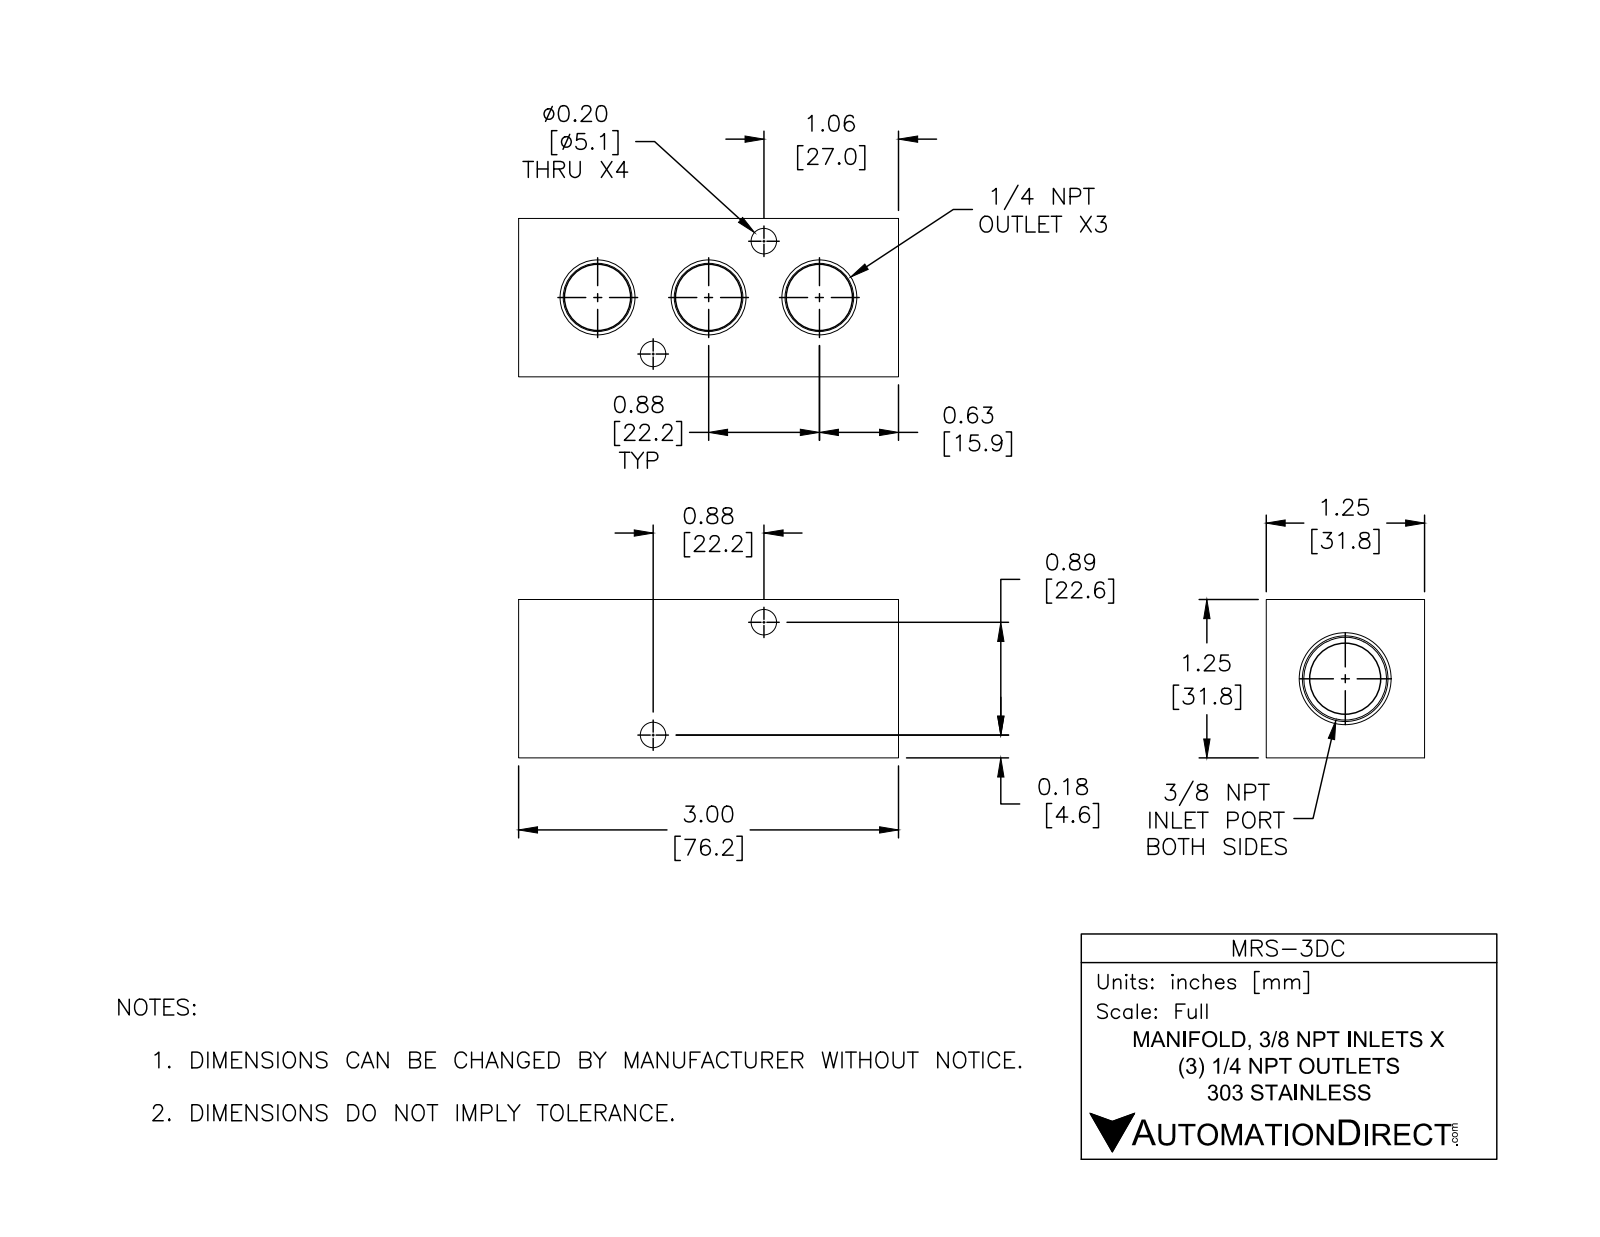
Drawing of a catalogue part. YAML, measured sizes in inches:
part_name: "MRS-3DC"
step_written_by: "SolidWorks 2015 (CONFIG_CONTROL_DESIGN)"
units: inches
bodies: {solids: 1, faces: 58, planar: 14, cylindrical: 24, other: 20}
overall_size: [3, 1.25, 1.25]
volume: 3.469
surface_area: 26.31
round_holes:
  - {diameter: 0.2, count: 4}
  - {diameter: 0.562, count: 1}
partial_cylinders:
  - {radius: 0.219, count: 3}
face_to_face_distances: [1.25, 3, 0.41, 2.59, 0.86, 0.39, 2.18]
hole_center_spacings: [1.248]
